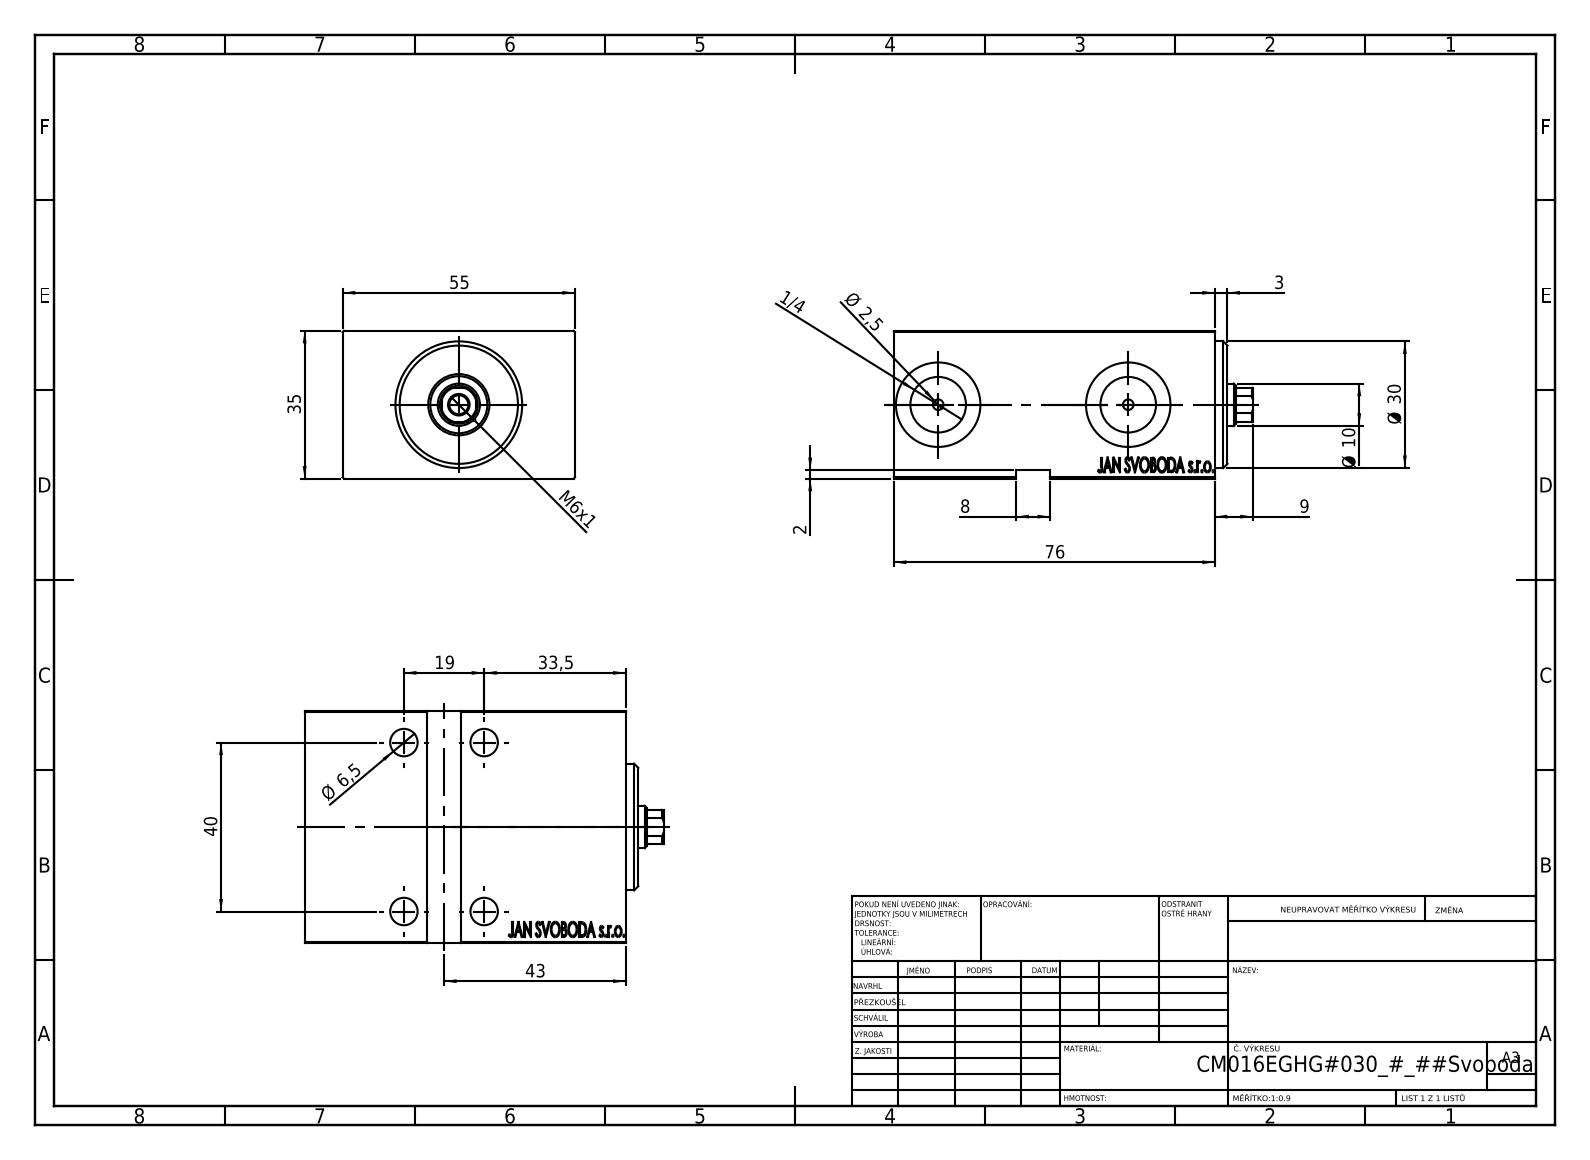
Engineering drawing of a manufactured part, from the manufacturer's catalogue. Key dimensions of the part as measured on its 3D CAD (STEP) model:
Part name (STEP PRODUCT): V450CM_VC_B; V450CM_E_Body; V450CM_E_VCP
STEP written by: SolidWorks 2019 (CONFIG_CONTROL_DESIGN)
Units: millimetres
Bodies: 3 solids, 859 faces (411 planar, 54 cylindrical, 394 other)
Overall size (bounding box): 85 × 55 × 35
Volume: 134 908 mm³ · Surface area: 32 565 mm²
Round holes (diameter × count): ⌀6.5 ×4, ⌀10.5 ×4, ⌀2.5 ×2, ⌀13.16 ×2, ⌀20 ×2, ⌀4.5 ×1, ⌀10 ×1, ⌀13.5 ×1, ⌀14.5 ×1, ⌀16 ×1, ⌀25 ×1
Round bosses / shafts (diameter × count): ⌀30 ×1, ⌀18 ×1
Partial cylindrical surfaces — rounded edges, fillets, slot ends (radius × count): R4.5 ×1
Main face-to-face distances: 35, 55, 76, 5, 71, 8, 3, 79, 2, 33
Hole centre spacings: 19, 40, 44.28, 45
